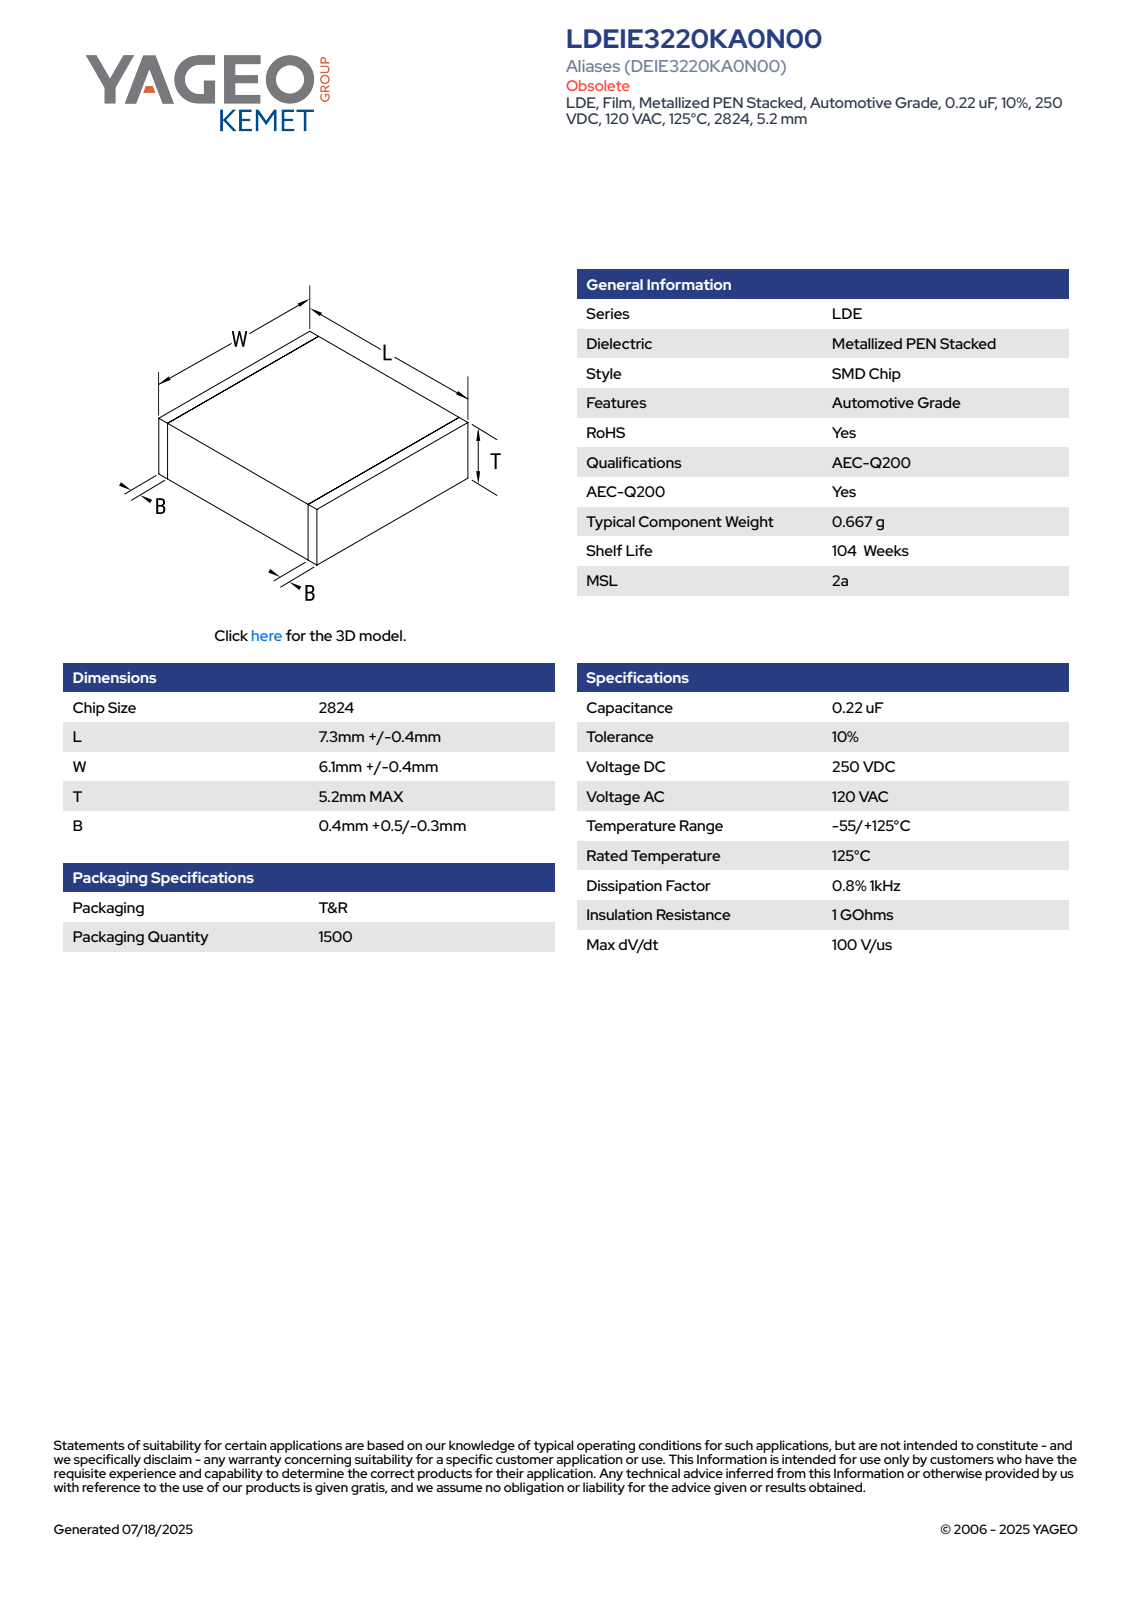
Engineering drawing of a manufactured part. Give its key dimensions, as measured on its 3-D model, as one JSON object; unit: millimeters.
{"part_name": "CFS_LDELDB_2824_L7.7W6.5T5.2B0.9", "step_written_by": "SolidWorks 2020 (AUTOMOTIVE_DESIGN)", "units": "millimeters", "bodies": {"solids": 4, "faces": 73, "planar": 73, "cylindrical": 0, "other": 0}, "overall_size": [7.7, 6.5, 5.2], "volume_mm3": 259, "surface_area_mm2": 251, "face_to_face_distances": [5.18, 6.48, 7.7, 5.19, 6.49, 5.2, 6.5, 0.5, 7.2, 6.7]}
